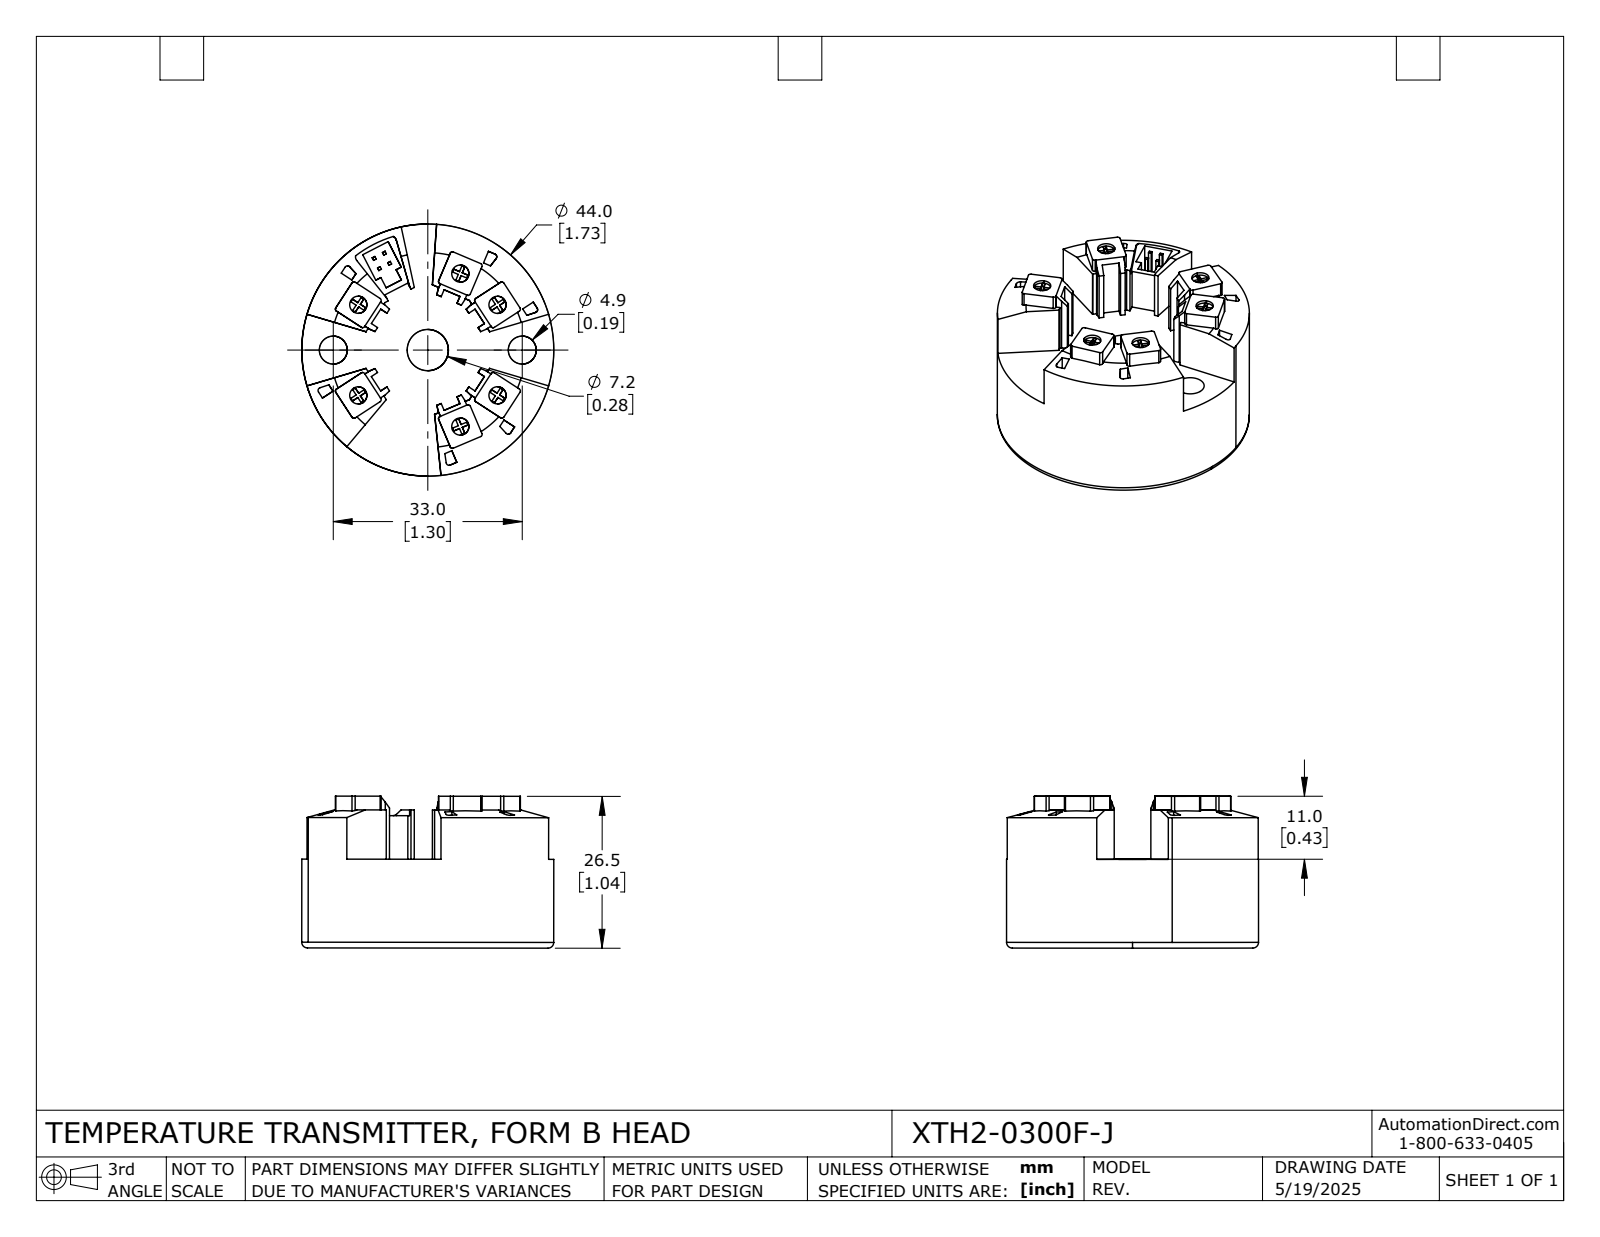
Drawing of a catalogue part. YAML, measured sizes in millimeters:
part_name: "XTDH2-0300F-J"
step_written_by: "SolidWorks 2024 (AUTOMOTIVE_DESIGN)"
units: millimeters
bodies: {solids: 1, faces: 341, planar: 281, cylindrical: 52, other: 8}
overall_size: [44, 44, 26.5]
volume: 28640
surface_area: 8684
round_holes:
  - {diameter: 3, count: 6}
  - {diameter: 4.9, count: 2}
  - {diameter: 7.2, count: 1}
round_bosses_or_shafts:
  - {diameter: 44, count: 1}
partial_cylinders:
  - {radius: 0.4, count: 24}
  - {radius: 0.5, count: 6}
  - {radius: 1, count: 2}
face_to_face_distances: [15.5, 26.5, 11, 1.5, 4.5, 1, 0.5, 3, 24.1, 8.6]
hole_center_spacings: [14.5, 8.5, 9, 9, 16.5, 17.2, 18.6, 22.2]
